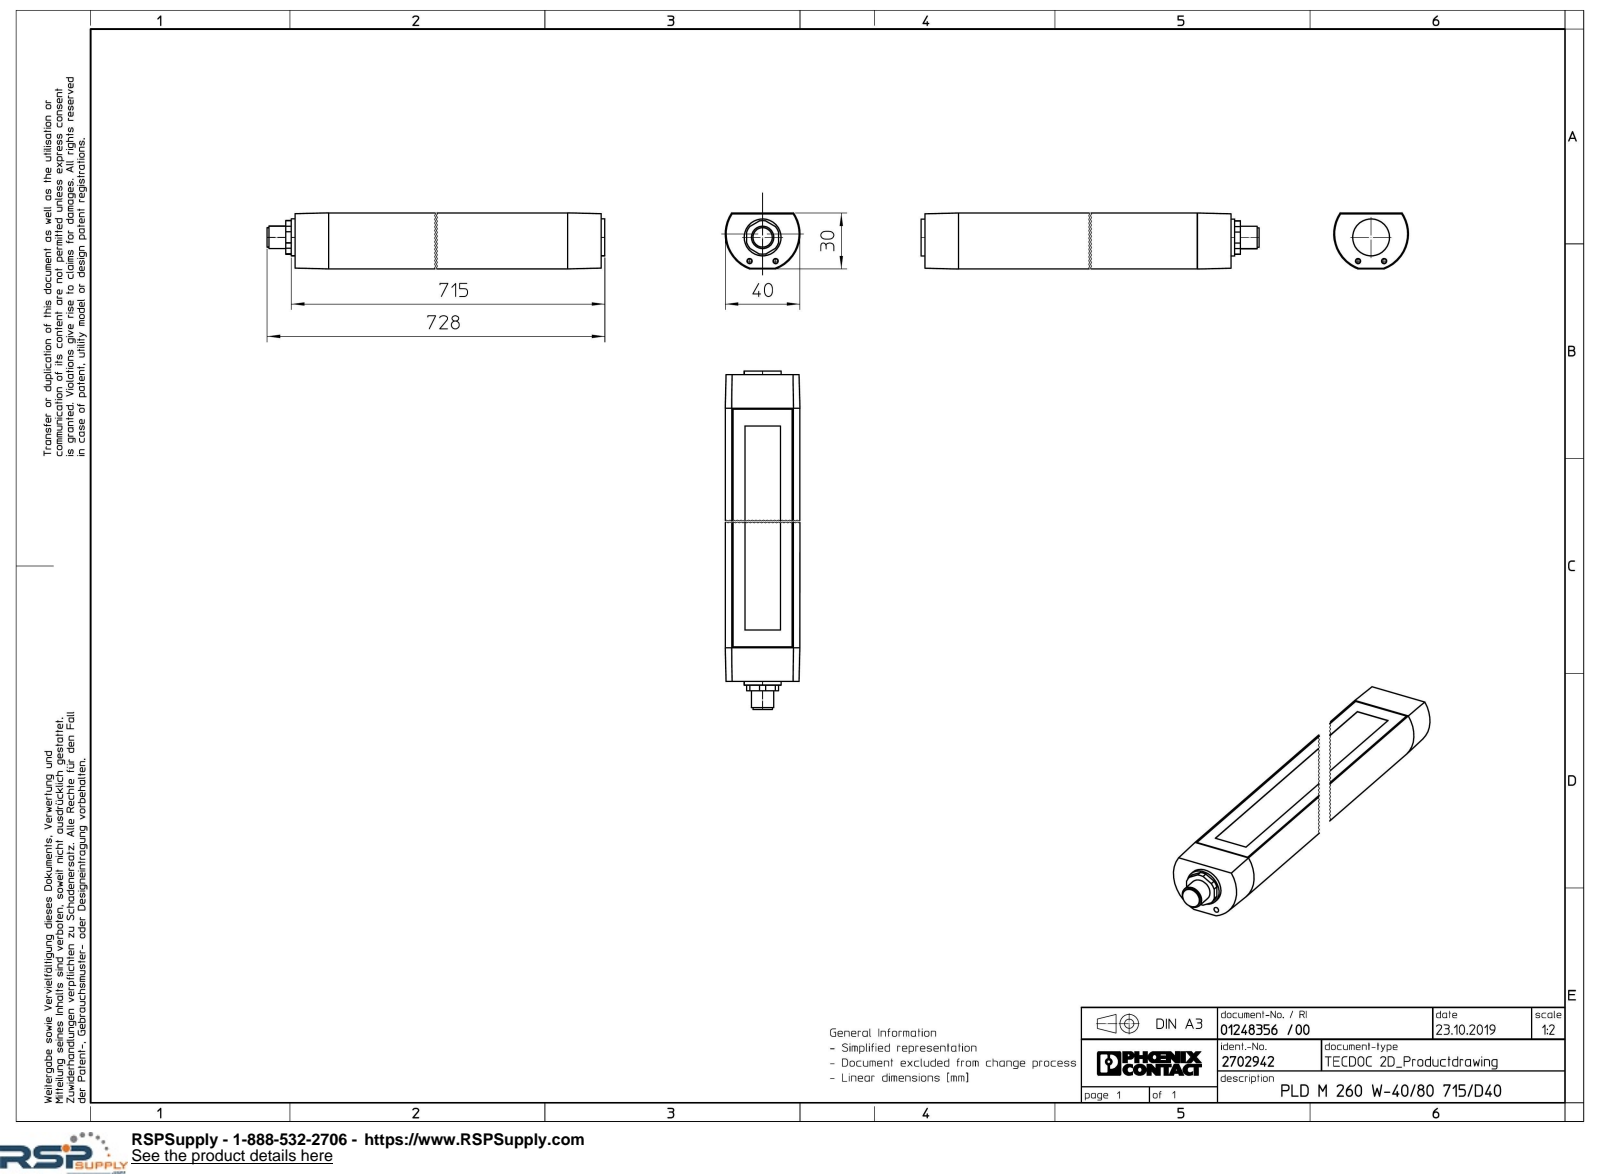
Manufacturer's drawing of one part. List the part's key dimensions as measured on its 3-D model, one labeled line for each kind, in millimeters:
Part name (STEP PRODUCT): PLD_M_260_W_40_80_715_D40-select
STEP written by: Creo Elements/Direct Modeling 20.1A 29-Sep-2018 (C) Parametric Technology GmbH (AUTOMOTIVE_DESIGN)
Units: millimetres
Bodies: 1 solid, 61 faces (33 planar, 16 cylindrical, 12 other)
Overall size (bounding box): 728 × 40 × 29.95
Volume: 737 923 mm³ · Surface area: 88 288 mm²
Round bosses / shafts (diameter × count): ⌀19.75 ×1, ⌀12 ×1, ⌀10.4 ×1
Partial cylindrical surfaces — rounded edges, fillets, slot ends (radius × count): R9 ×1, R20 ×1
Main face-to-face distances: 29.75, 29.85, 29.95, 711, 2, 713, 46.13, 46.15, 6.3, 25.3
